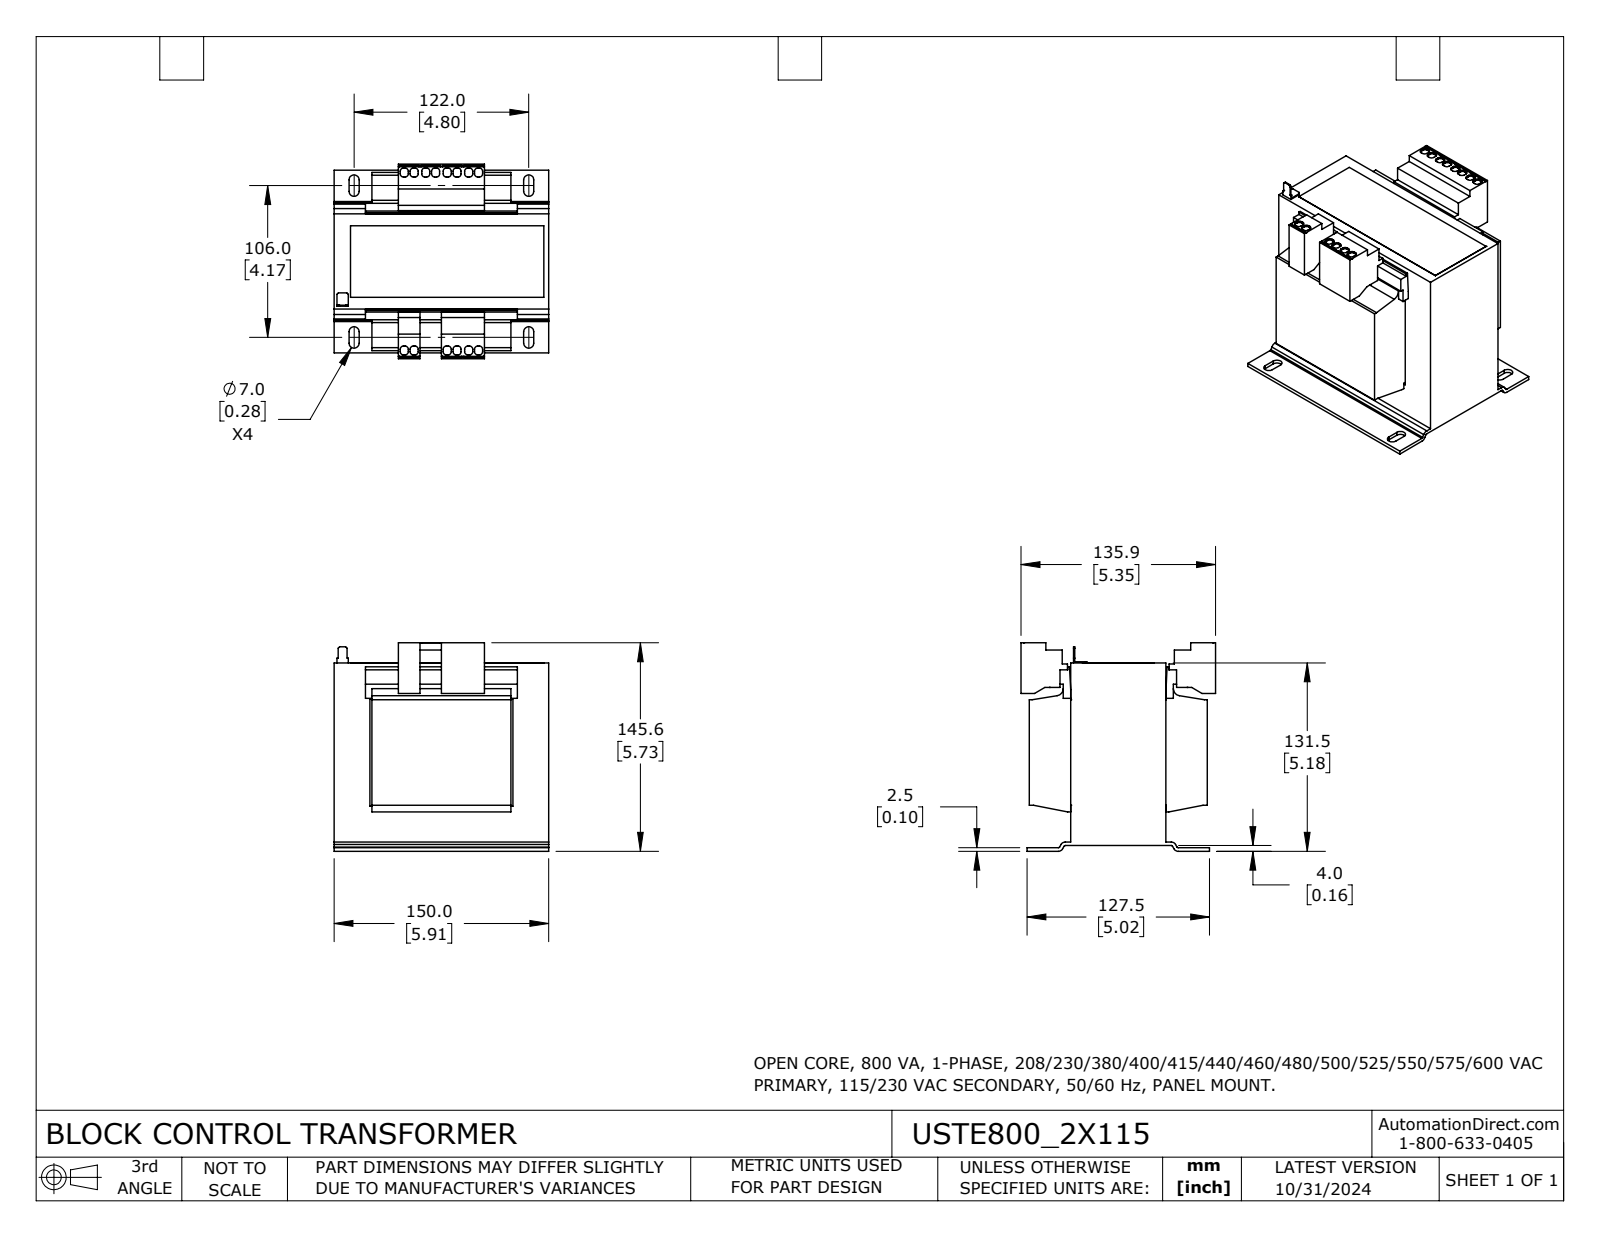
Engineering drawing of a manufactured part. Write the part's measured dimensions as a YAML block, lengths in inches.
part_name: "USTE800_2X115"
step_written_by: "SolidWorks 2023 (CONFIG_CONTROL_DESIGN)"
units: inches
bodies: {solids: 1, faces: 433, planar: 355, cylindrical: 78, other: 0}
overall_size: [5.906, 5.731, 5.35]
volume: 110.8
surface_area: 287.3
partial_cylinders:
  - {radius: 0.087, count: 56}
  - {radius: 0.138, count: 12}
  - {radius: 0.039, count: 4}
  - {radius: 0.197, count: 2}
face_to_face_distances: [1.039, 4.866, 1.14, 3.758, 0.984, 2.618, 4.921, 0.055, 3.882, 3.827]
